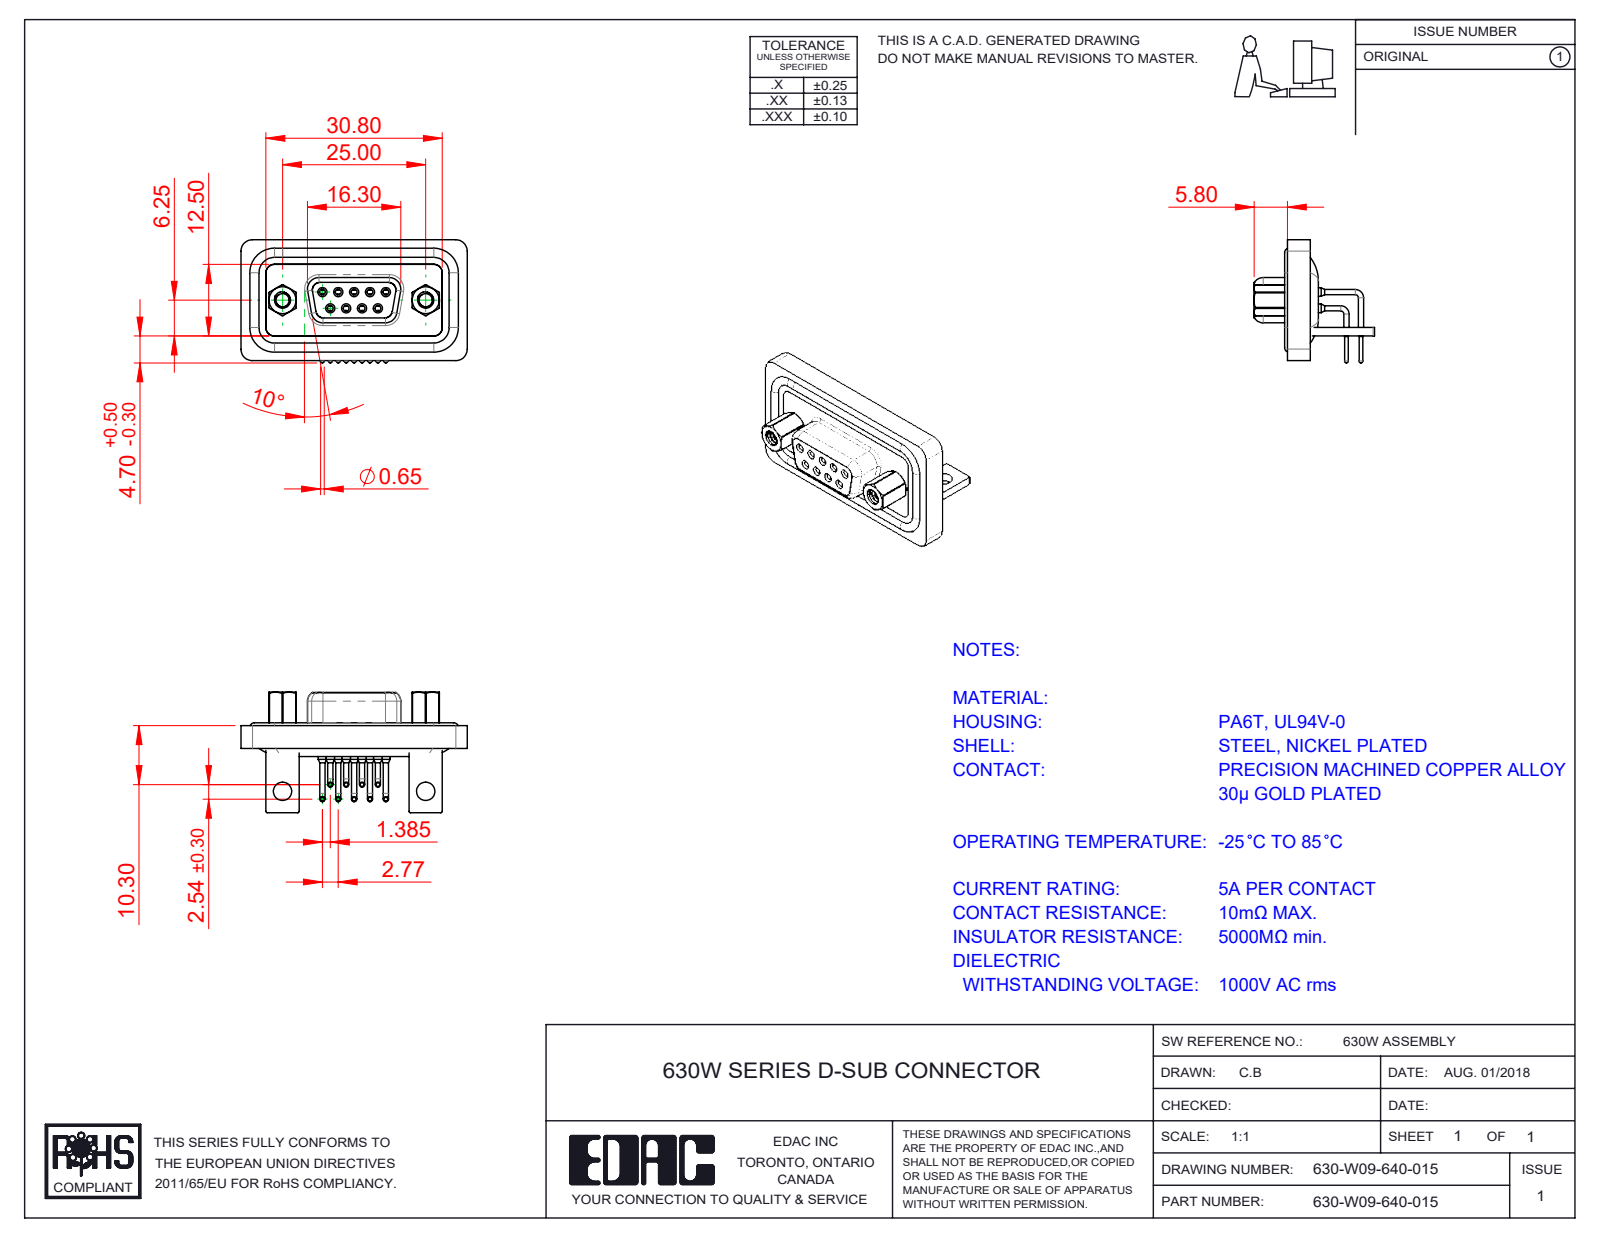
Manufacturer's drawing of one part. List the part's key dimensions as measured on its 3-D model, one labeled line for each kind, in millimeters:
Part name (STEP PRODUCT): 630W 4-40 Hex Standoff; 630W Shell_09 Contacts; 630-W09-640-015; 630W Contact Row 1 (+5 more)
STEP written by: SolidWorks 2023 (CONFIG_CONTROL_DESIGN)
Units: millimetres
Bodies: 19 solids, 966 faces (258 planar, 469 cylindrical, 239 other)
Overall size (bounding box): 39.51 × 21.5 × 21.5
Volume: 4 711 mm³ · Surface area: 8 055 mm²
Round holes (diameter × count): ⌀1 ×9, ⌀1.1 ×9, ⌀1.5 ×9, ⌀1.7 ×9, ⌀1.8 ×9, ⌀2 ×9, ⌀2.26 ×2, ⌀2.29 ×2, ⌀3.2 ×2, ⌀4 ×2, ⌀4.8 ×2, ⌀4.9 ×2
Round bosses / shafts (diameter × count): ⌀0.9 ×18, ⌀1.6 ×13, ⌀0.65 ×9, ⌀1.5 ×4, ⌀2.79 ×2, ⌀5 ×1
Partial cylindrical surfaces — rounded edges, fillets, slot ends (radius × count): R2 ×15, R1.5 ×14, R0.25 ×12, R1.35 ×8, R2.7 ×6, R0.5 ×5, R0.9 ×4, R1.6 ×4
Main face-to-face distances: 0.4, 1.6, 1.1, 1.8, 4.3, 2.9, 2.5, 1.5, 5.8, 0.5
Hole centre spacings: 3.16, 2.77, 5.54, 5.03, 5.04, 7.48, 7.49, 8.31
